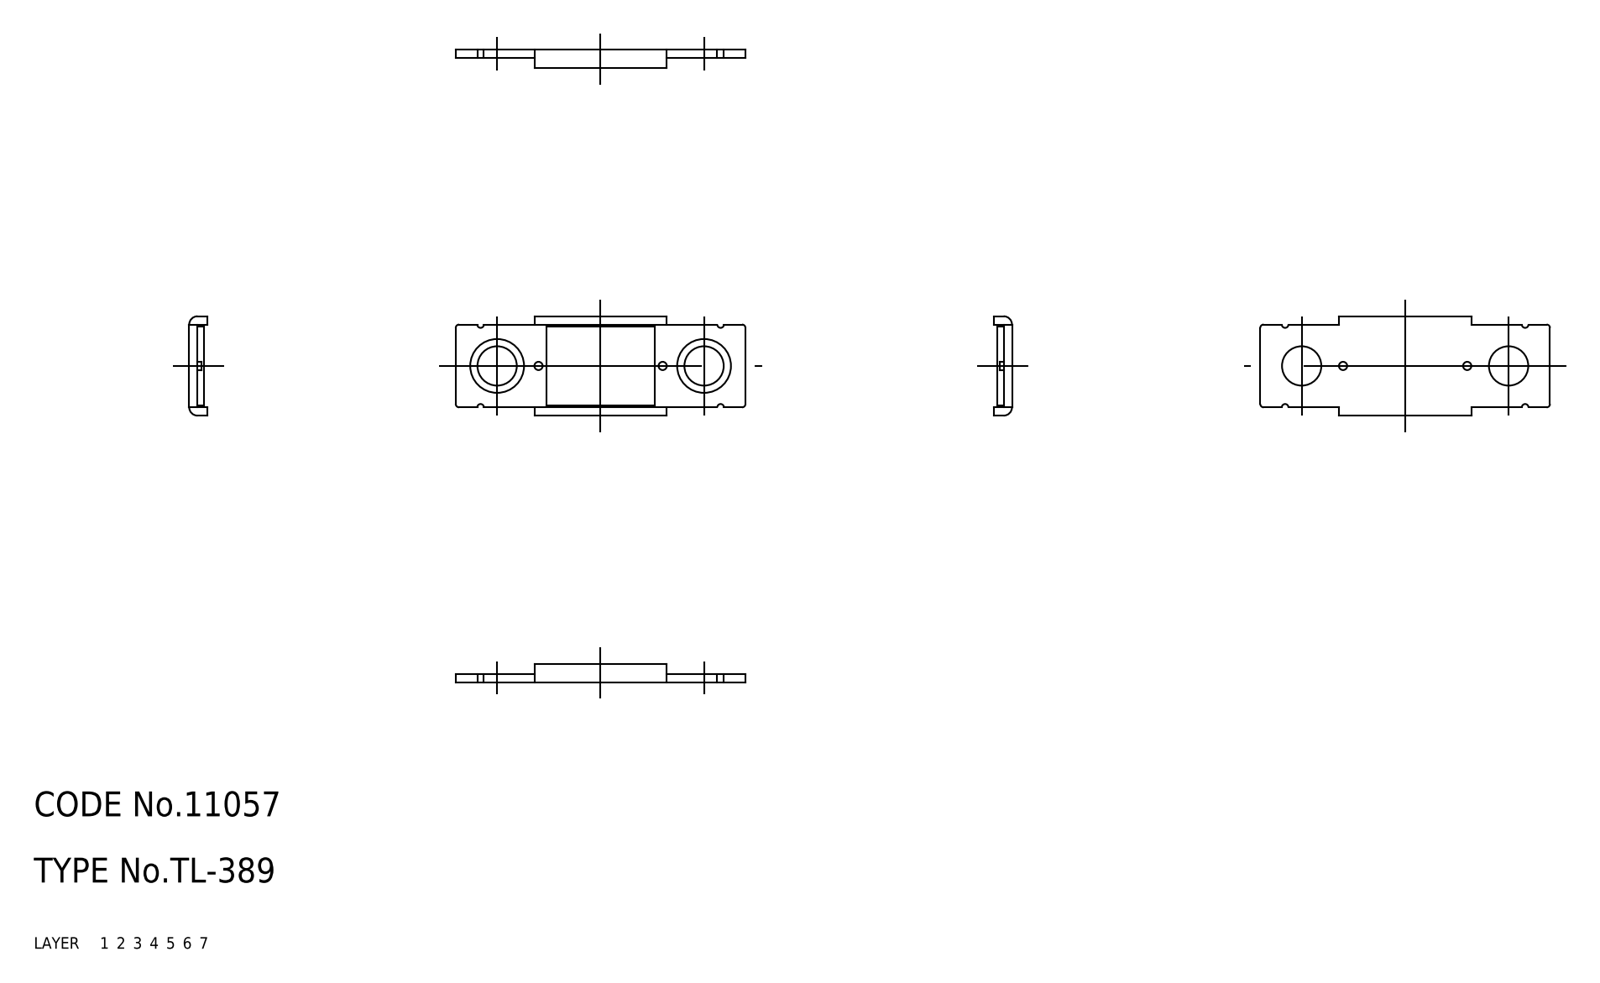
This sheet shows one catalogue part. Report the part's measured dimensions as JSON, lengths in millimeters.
{"part_name": "67111610", "step_written_by": "CADfix (AUTOMOTIVE_DESIGN)", "units": "millimeters", "bodies": {"solids": 1, "faces": 57, "planar": 0, "cylindrical": 0, "other": 57}, "overall_size": [35, 12, 2.2], "volume_mm3": 463, "surface_area_mm2": 912}
